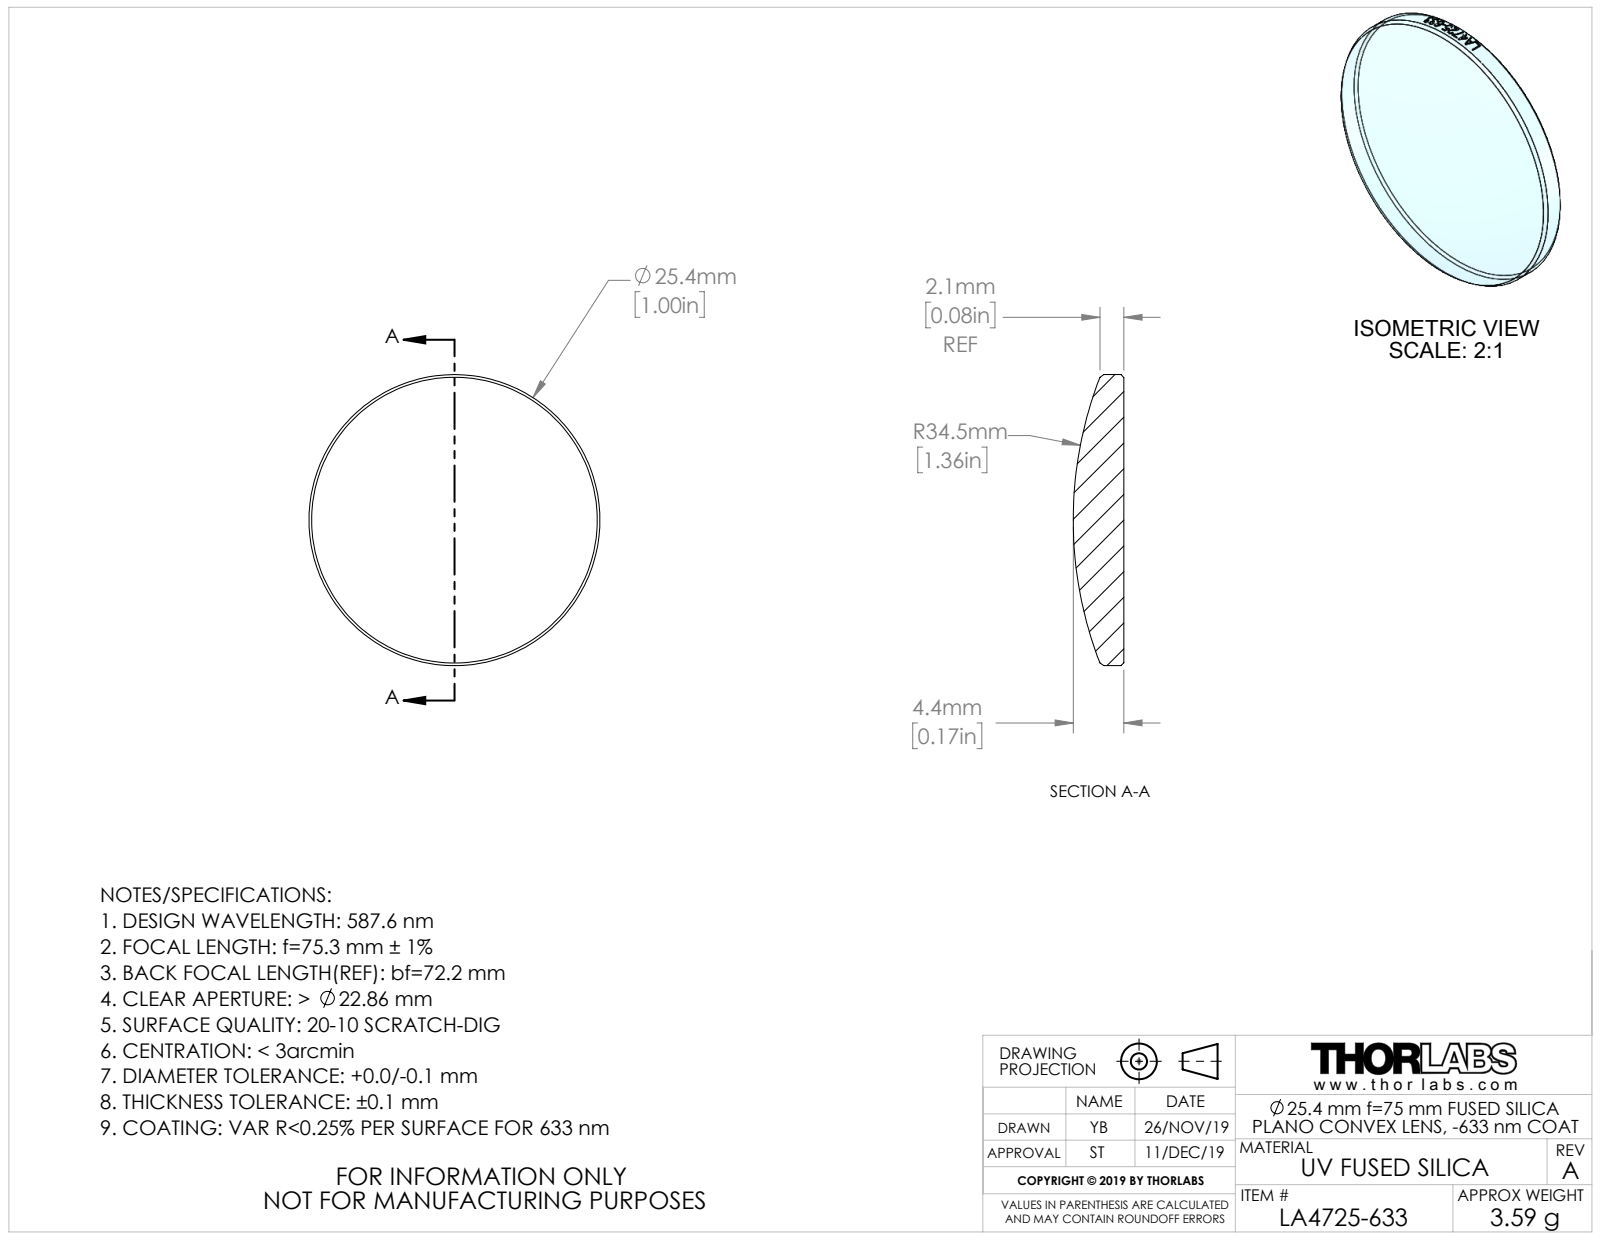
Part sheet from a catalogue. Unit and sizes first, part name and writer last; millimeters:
Units: millimetres
Overall size (bounding box): 25.4 × 25.4 × 4.42
Round bosses / shafts (diameter × count): ⌀25.4 ×1
Volume: 1 629 mm³ · Surface area: 1 173 mm²
Bodies: 1 solid, 27 faces (1 planar, 20 cylindrical, 6 other)
Part name (STEP PRODUCT): CTN014987-999; CTN015006
STEP written by: SolidWorks 2018 (AUTOMOTIVE_DESIGN)
